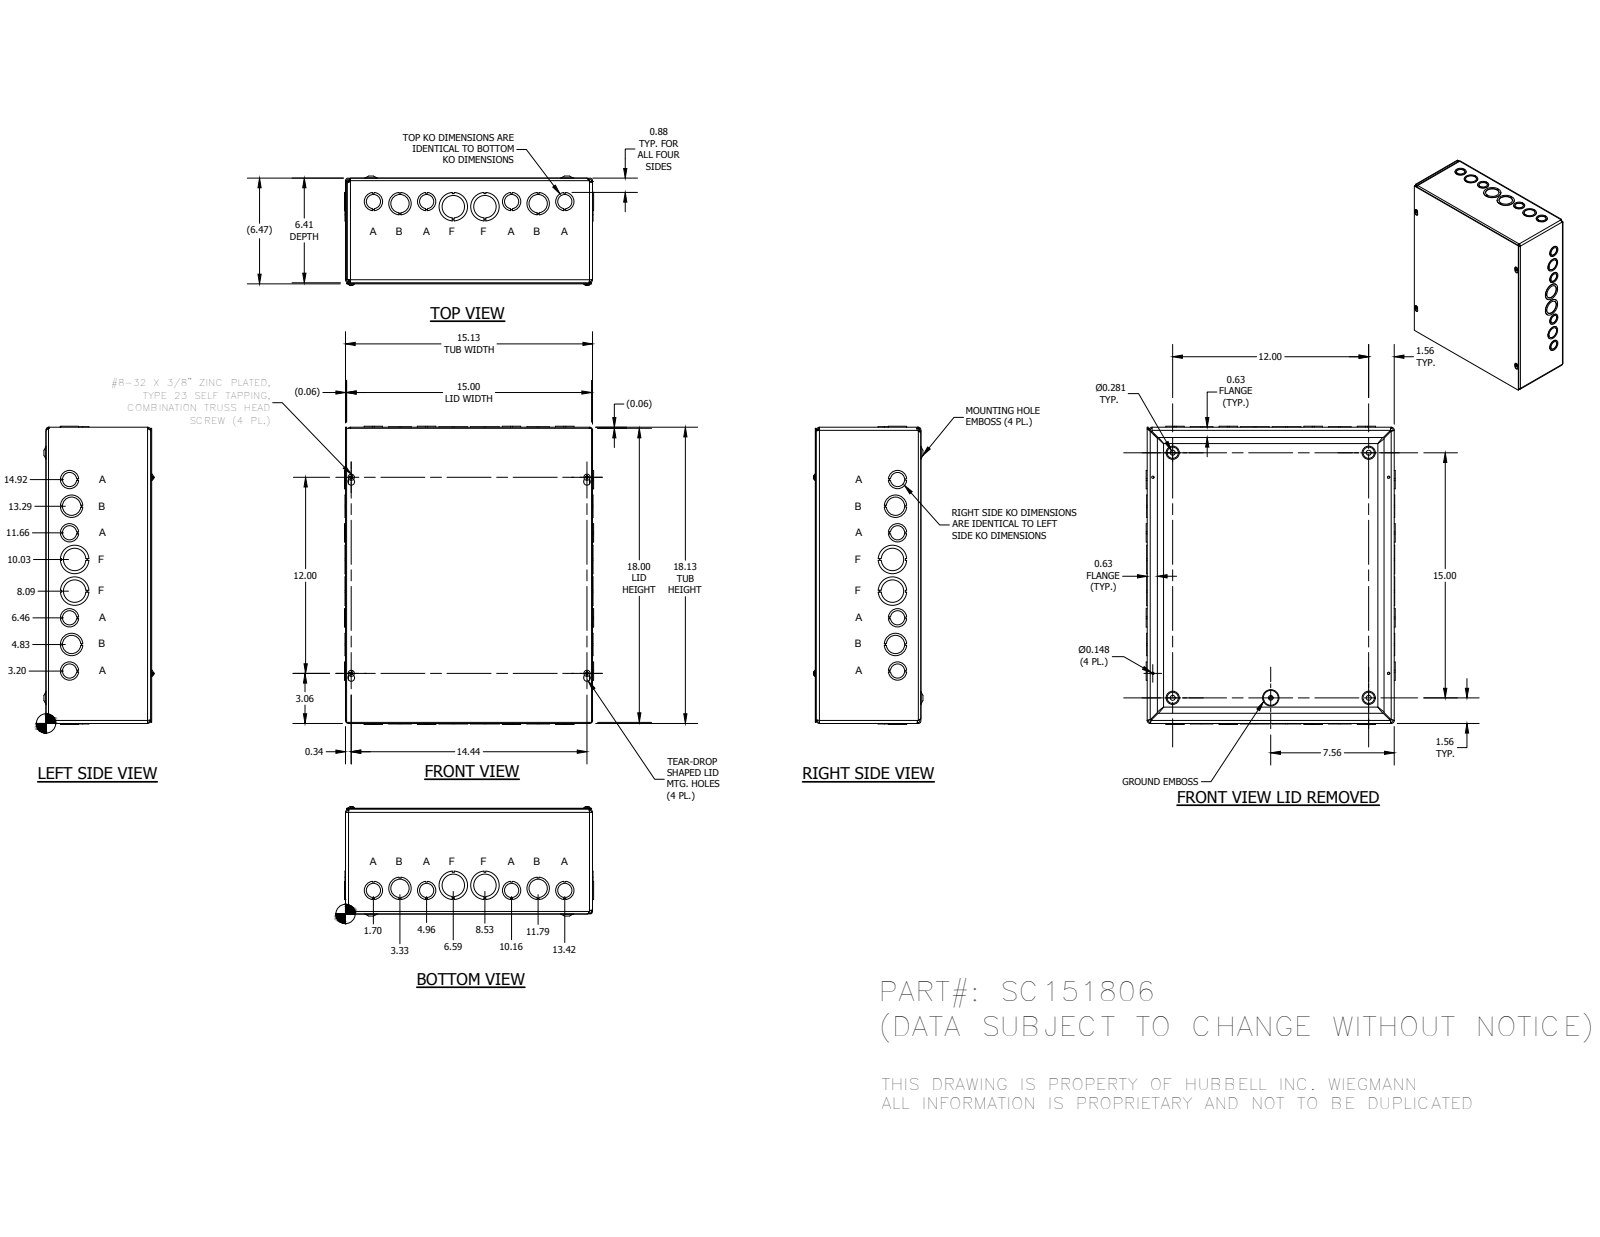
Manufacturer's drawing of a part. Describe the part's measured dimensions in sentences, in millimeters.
The part is named "SC1518BKP; SC151806WRA; SC1518LID; 34056 (+1 more)". Its 3-D file was written by "Autodesk Inventor 2014 (AUTOMOTIVE_DESIGN)". It is 38 solids with 1254 faces: 837 planar, 259 cylindrical and 158 other. Overall it measures 463.52 by 387.32 by 170 millimeters. Round holes: 12 of diameter 28.57, 8 of diameter 22.22, 8 of diameter 34.92, 4 of diameter 3.76, 4 of diameter 7.62, 4 of diameter 44.45, 1 of diameter 4.19. Round bosses or shafts: 4 of diameter 9.75, 4 of diameter 4.17, 1 of diameter 5.8. Partial cylindrical surfaces (rounded edges, fillets, slot ends): 12 of radius 3.17, 8 of radius 4.75, 4 of radius 1.4, 4 of radius 1.57, 4 of radius 2.38, 4 of radius 2.97, 4 of radius 3.15, 4 of radius 3.96. The main face-to-face distances are 1.57, 161.12, 162.69, 1.59, 162.71, 164.28, 458.8, 1.58, 384.18, 382.6. The hole center spacings are 41.52, 42.15, 49.09, 82.94, 91.03, 132.17, 173.51, 214.88.
